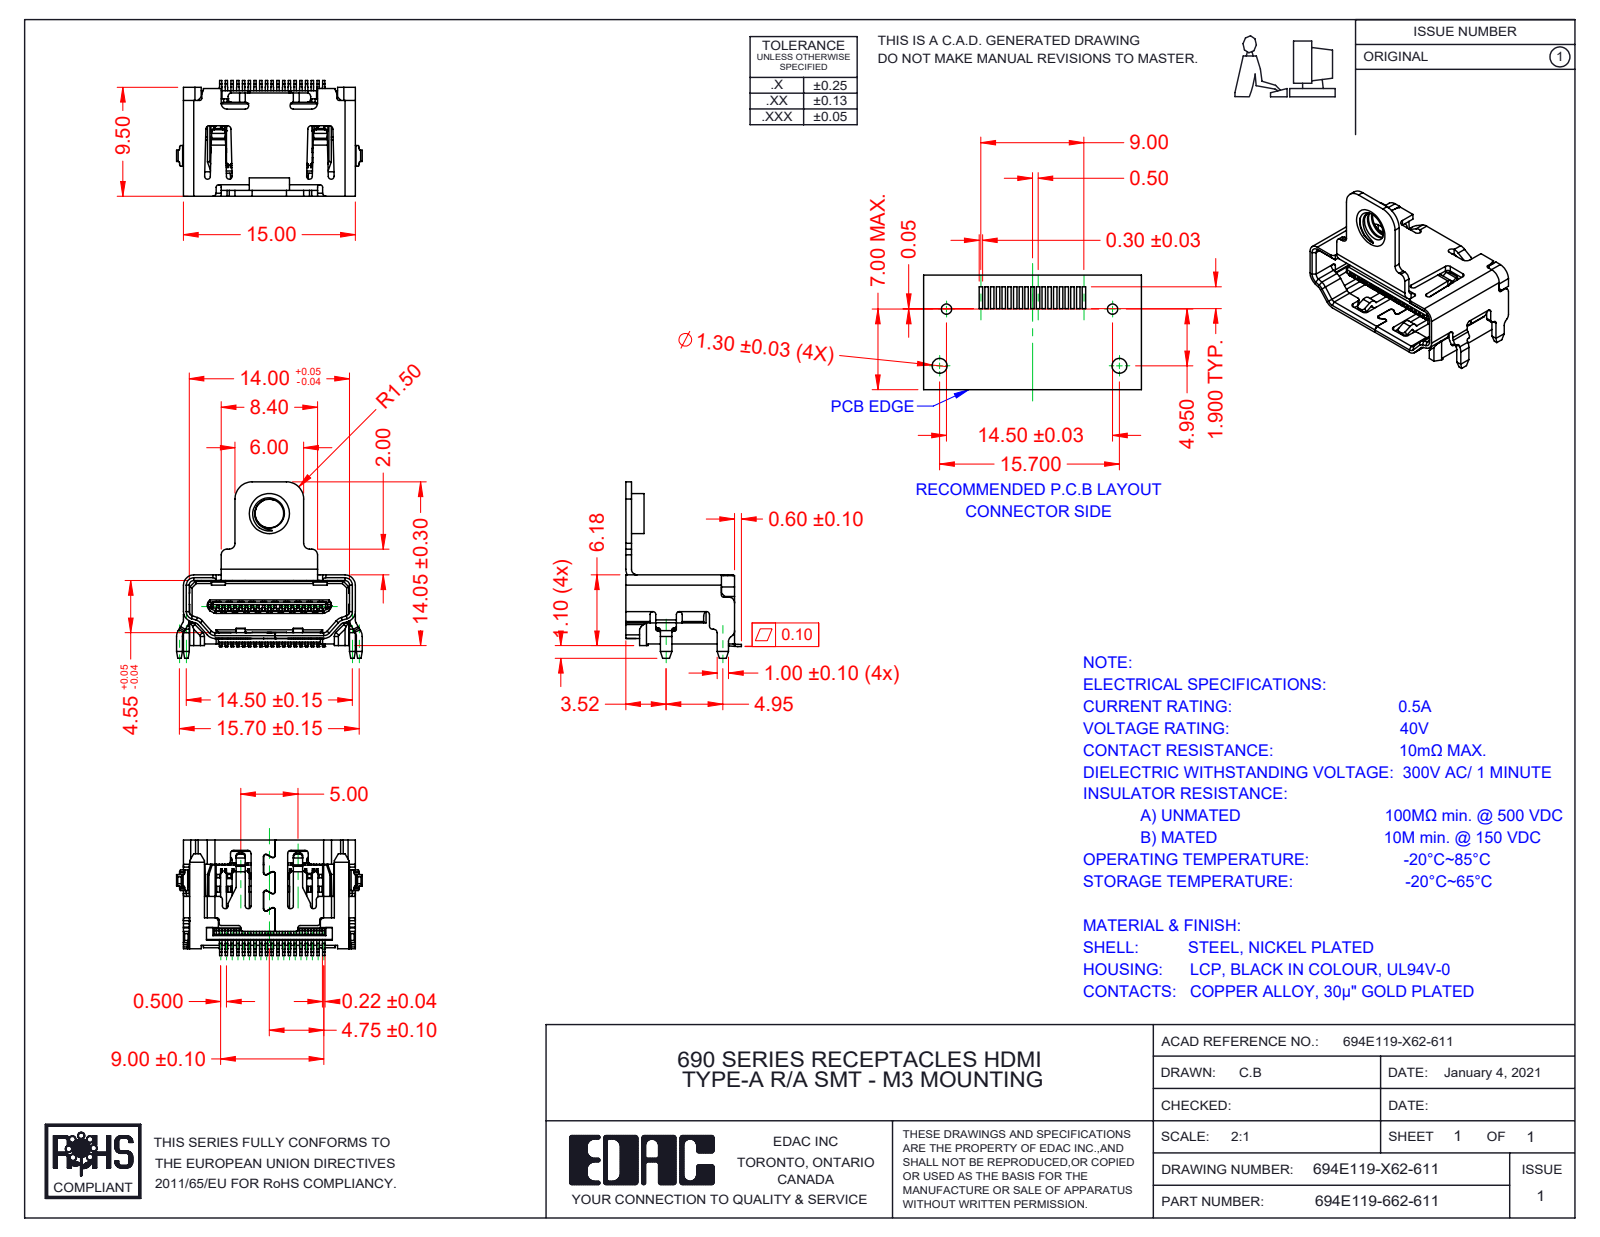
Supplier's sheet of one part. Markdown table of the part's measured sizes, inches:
| quantity | value |
| --- | --- |
| part name | Contact Lower 694E119-X62-611; Contact Upper 694E119-X62-611; Shell 694E119-X62-611; 694E119-162-611 (+1 more) |
| STEP written by | SolidWorks 2020 (AUTOMOTIVE_DESIGN) |
| units | inches |
| bodies | 21 solids, 2892 faces (1971 planar, 793 cylindrical, 128 other) |
| overall size | 0.638 × 0.606 × 0.398 |
| volume | 0.023 in³ |
| surface area | 2.427 in² |
| round holes (diameter × count) | 0.098 × 1 |
| round bosses / shafts (diameter × count) | 0.138 × 1 |
| partial cylindrical surfaces (radius × count) | 0.008 × 35, 0.012 × 24, 0.02 × 22, 0.01 × 19, 0.006 × 18, 0.039 × 11, 0.014 × 8, 0.016 × 8 |
| main face-to-face distances | 0.02, 0.099, 0.019, 0.08, 0.119, 0.094, 0.571, 0.022, 0.1, 0.199 |
